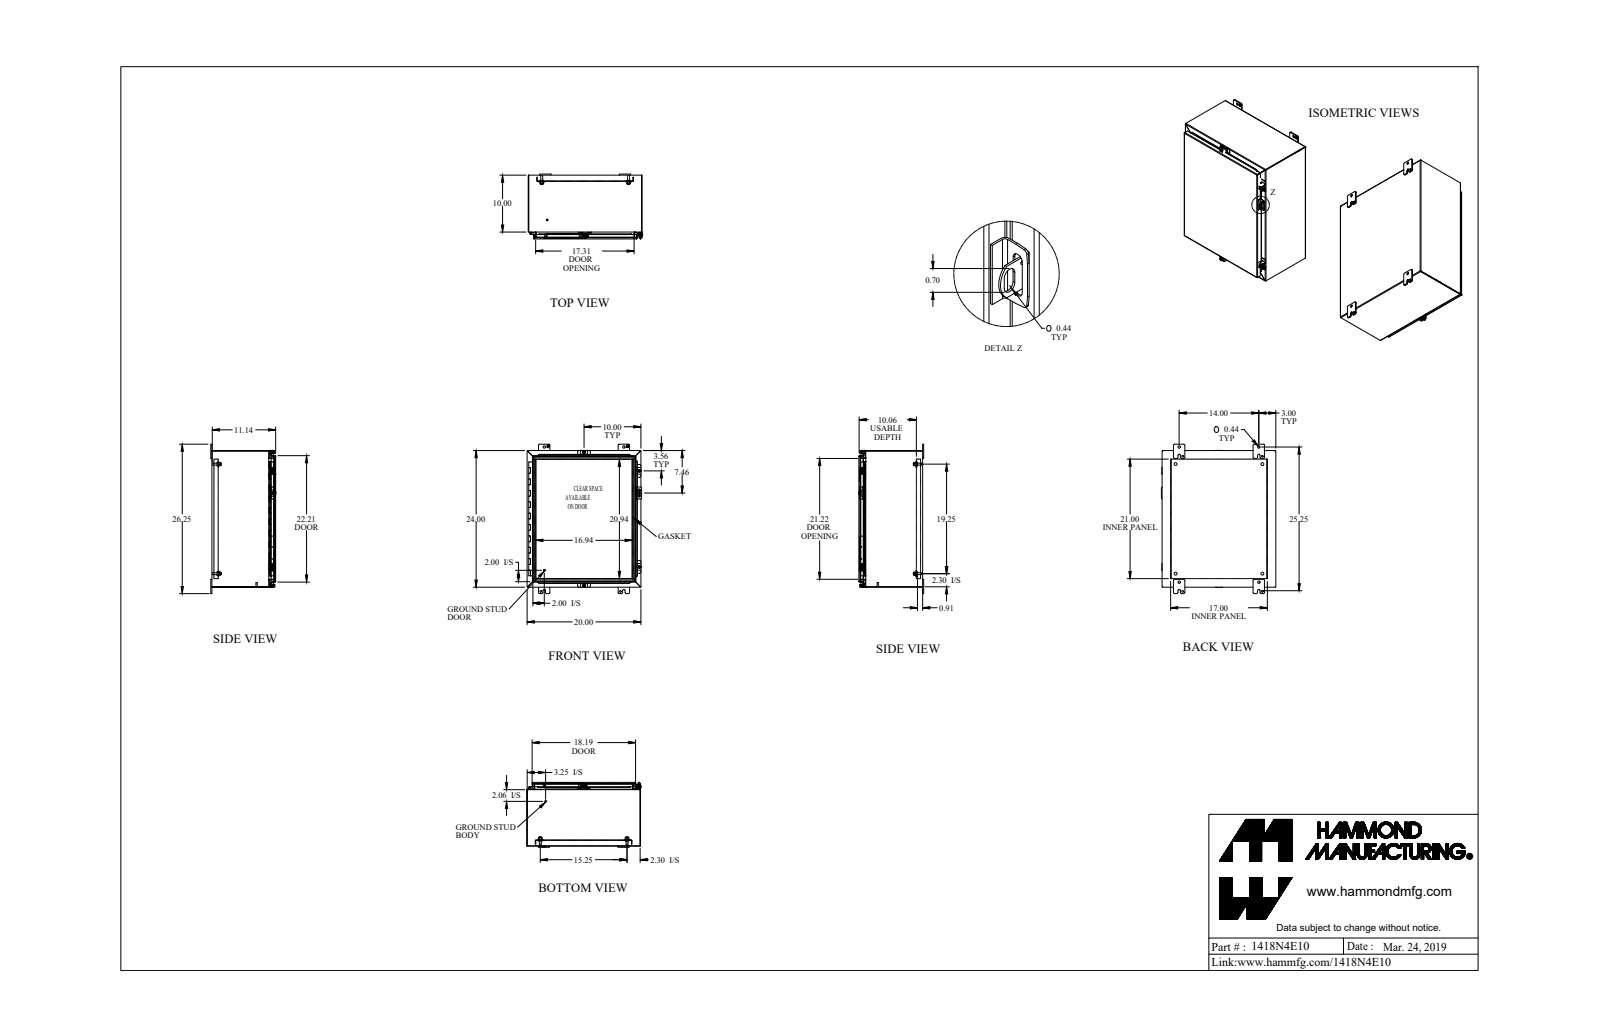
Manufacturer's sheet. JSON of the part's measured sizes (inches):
{"part_name": "1418N4E10_Default", "step_written_by": "SolidWorks 2019 (CONFIG_CONTROL_DESIGN)", "units": "inches", "bodies": {"solids": 39, "faces": 1411, "planar": 853, "cylindrical": 473, "other": 85}, "overall_size": [26.25, 20.126, 11.437], "volume_in3": 198.5, "surface_area_in2": 5224, "round_holes": [[0.213, 4], [0.313, 4], [0.375, 4], [0.437, 4], [0.5, 4], [0.265, 2], [0.265, 2], [0.307, 2], [0.445, 2], [0.125, 1], [0.187, 1]], "round_bosses_or_shafts": [[0.65, 4], [0.5, 4], [0.39, 4], [0.375, 4], [0.33, 4], [0.244, 4], [1, 2], [0.281, 2]], "partial_cylinders_radius": [[0.188, 26], [0.036, 24], [0.108, 24], [0.048, 21], [0.143, 21], [0.25, 20], [0.125, 10], [0.045, 8]], "face_to_face_distances": [0.072, 19.928, 0.072, 11.066, 11.138, 11.138, 11.21, 23.928, 0.095, 10.106], "hole_center_spacings": [7.916, 14, 22.694, 24.559, 1.625, 7.915, 15.25, 17.416]}
